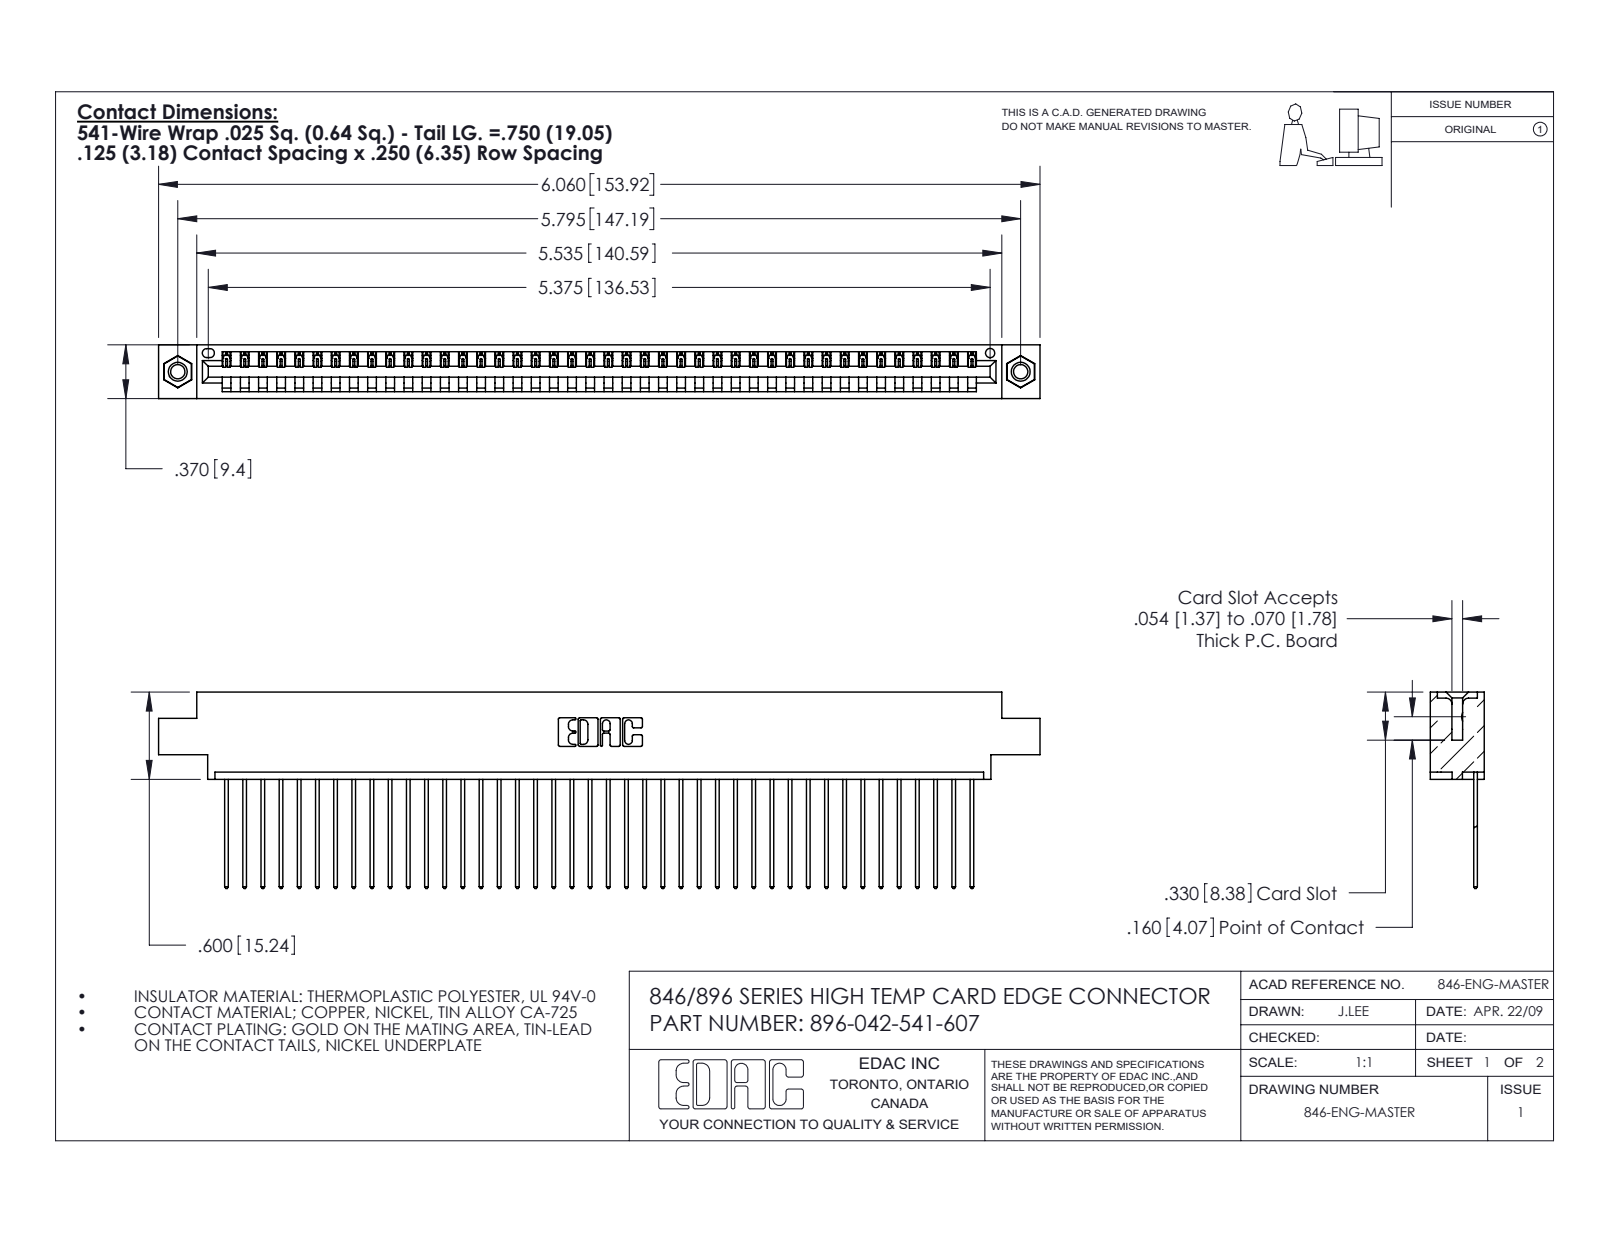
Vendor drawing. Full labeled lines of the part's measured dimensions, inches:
Part name (STEP PRODUCT): 396-042-541-607; 346 Part_0.170 Offset - 0.156 Dia-TI; 345-292-001_345-293-141; 345-250-001_345-250-005-103
STEP written by: SolidWorks 2016 (CONFIG_CONTROL_DESIGN)
Units: inches
Bodies: 45 solids, 2622 faces (1792 planar, 814 cylindrical, 16 other)
Overall size (bounding box): 6.06 × 1.35 × 0.37
Volume: 0.897 in³ · Surface area: 30.07 in²
Round holes (diameter × count): ⌀0.098 ×2, ⌀0.125 ×2, ⌀0.156 ×2, ⌀0.064 ×1
Round bosses / shafts (diameter × count): ⌀0.155 ×2
Partial cylindrical surfaces — rounded edges, fillets, slot ends (radius × count): R0.006 ×84, R0.01 ×84, R0.01 ×22, R0.007 ×6, R0.031 ×6, R0.026 ×3, R0.031 ×2, R0.04 ×2
Main face-to-face distances: 0.048, 0.322, 0.37, 0.25, 0.072, 0.298, 0.025, 0.222, 0.148, 0.1
Hole centre spacings: 0.246, 5.586, 5.795
